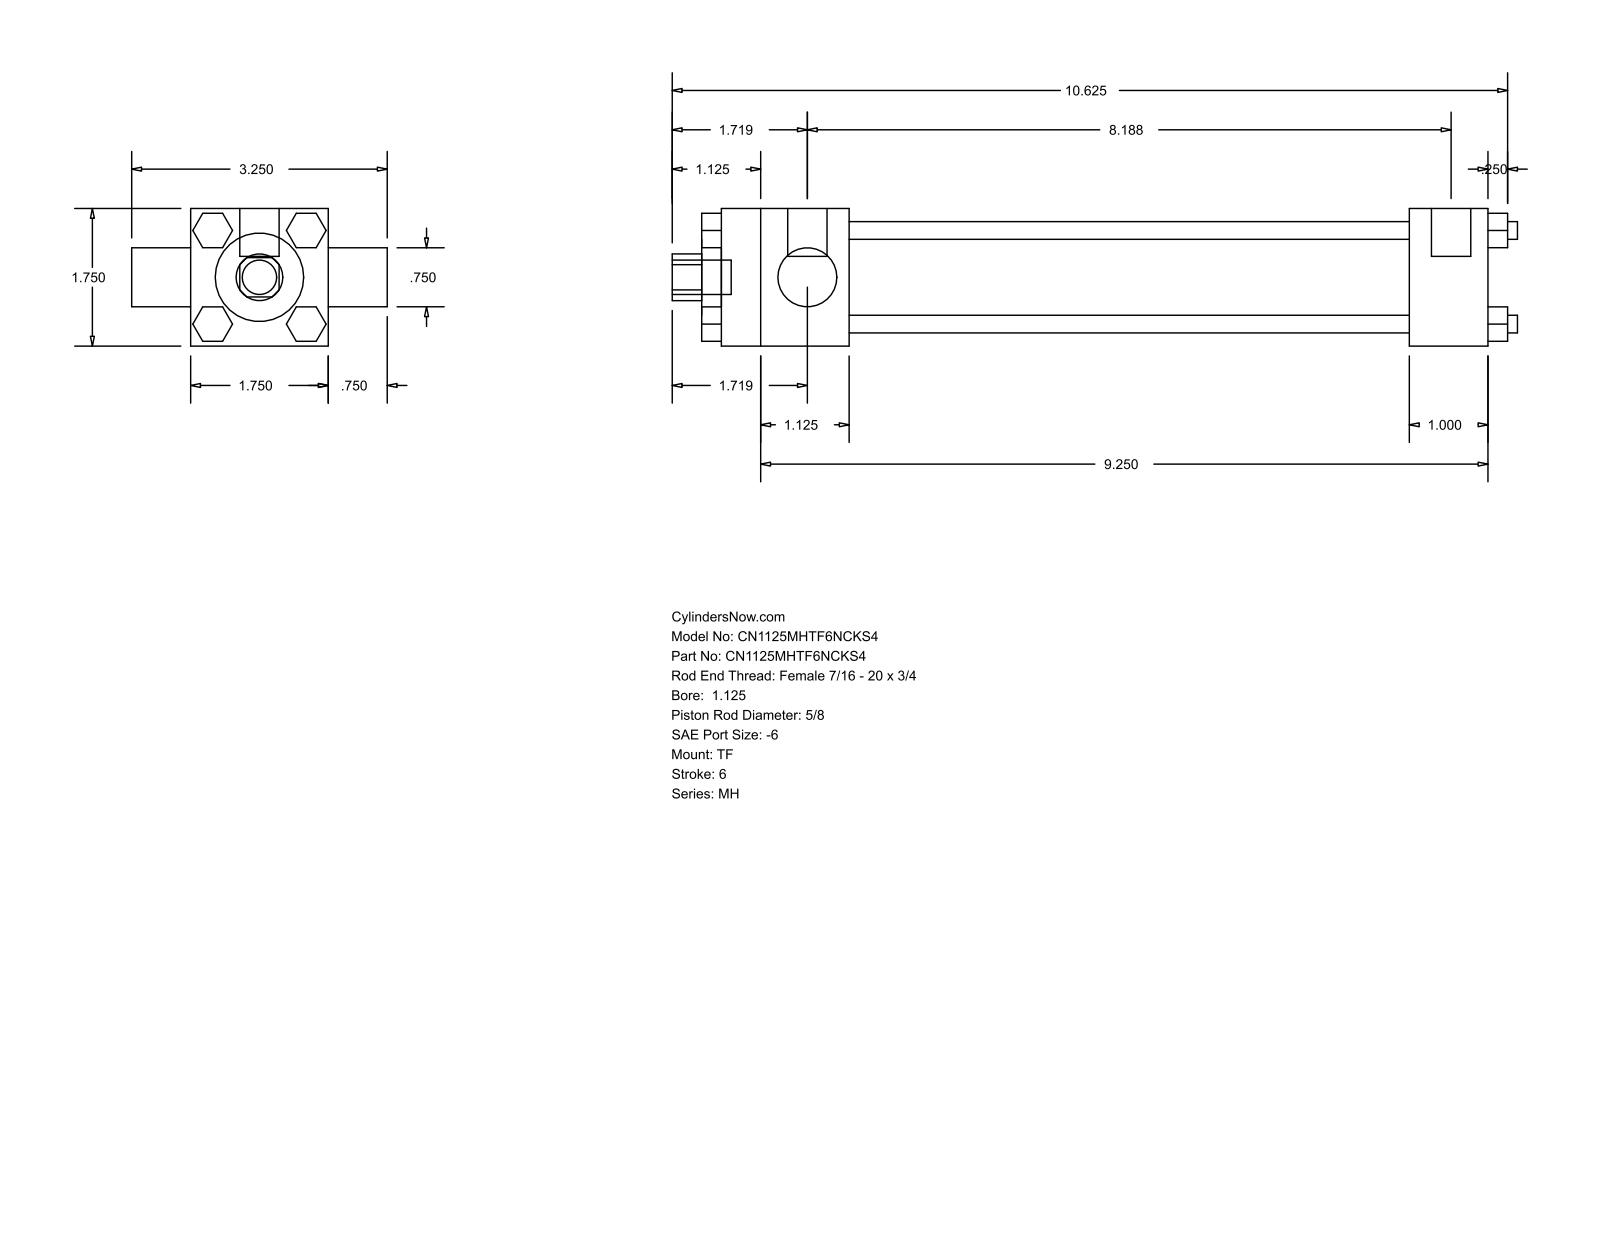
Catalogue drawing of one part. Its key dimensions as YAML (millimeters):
part_name: "MH_TF__0112_0.625"
step_written_by: "GSSL Pune (CONFIG_CONTROL_DESIGN)"
units: millimeters
bodies: {solids: 0, faces: 120, planar: 92, cylindrical: 28, other: 0}
overall_size: [273.05, 82.55, 44.45]
round_holes:
  - {diameter: 15.88, count: 1}
  - {diameter: 19.05, count: 1}
  - {diameter: 28.57, count: 1}
  - {diameter: 34.92, count: 1}
round_bosses_or_shafts:
  - {diameter: 5.71, count: 4}
  - {diameter: 5.56, count: 3}
  - {diameter: 12.7, count: 2}
  - {diameter: 11.11, count: 1}
partial_cylinders:
  - {radius: 7.54, count: 1}
face_to_face_distances: [44.46, 11.11, 180.97, 206.37, 25.4, 41.27, 222.24, 247.64, 47.62, 6.35]
